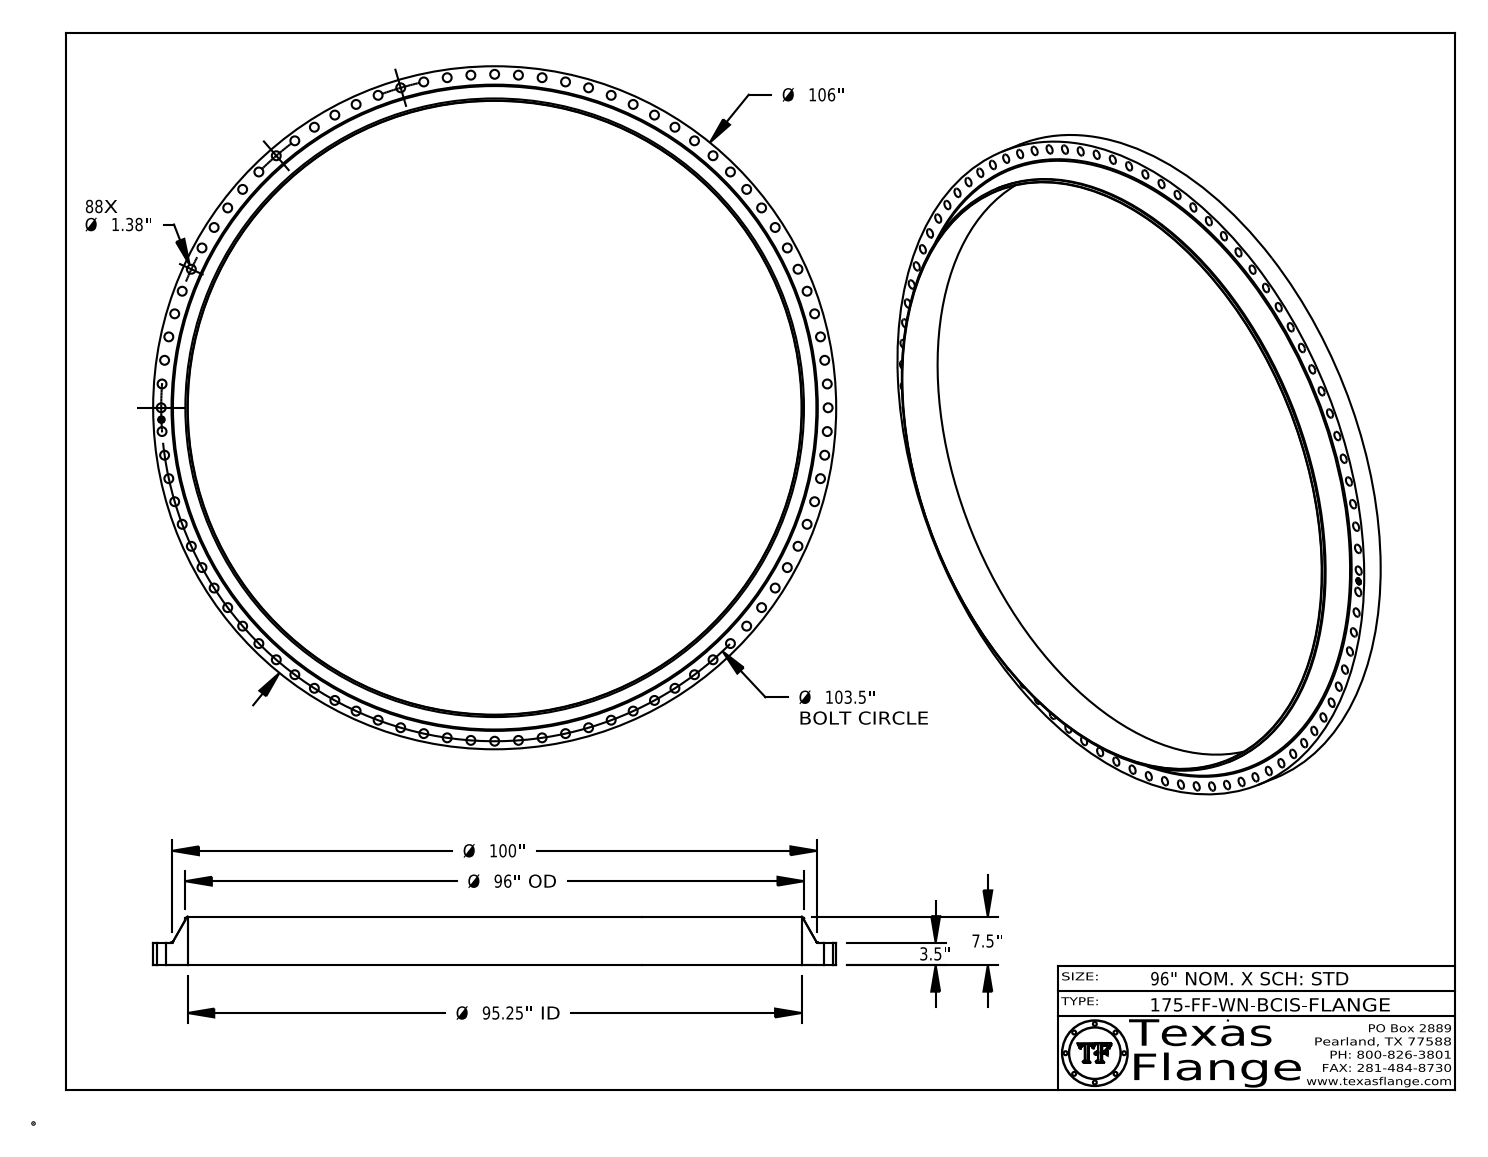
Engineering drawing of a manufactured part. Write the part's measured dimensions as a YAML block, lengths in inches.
part_name: "175-FF-WN, BCIS"
step_written_by: "CATIA V5 STEP AP214 (AUTOMOTIVE_DESIGN)"
units: inches
bodies: {solids: 1, faces: 576, planar: 368, cylindrical: 202, other: 6}
overall_size: [106, 106, 7.5]
volume: 7004
surface_area: 8599
round_holes:
  - {diameter: 1.38, count: 88}
  - {diameter: 1, count: 1}
  - {diameter: 95.25, count: 1}
round_bosses_or_shafts:
  - {diameter: 0.061, count: 8}
  - {diameter: 106, count: 1}
  - {diameter: 96, count: 1}
  - {diameter: 0.788, count: 1}
face_to_face_distances: [3.5, 7.5, 4, 0.015, 3.485, 4.015, 0.298, 0.292, 0.054, 0.193]
hole_center_spacings: [51.75, 3.694, 103.237, 102.907, 7.383, 102.447, 103.434, 11.064]
